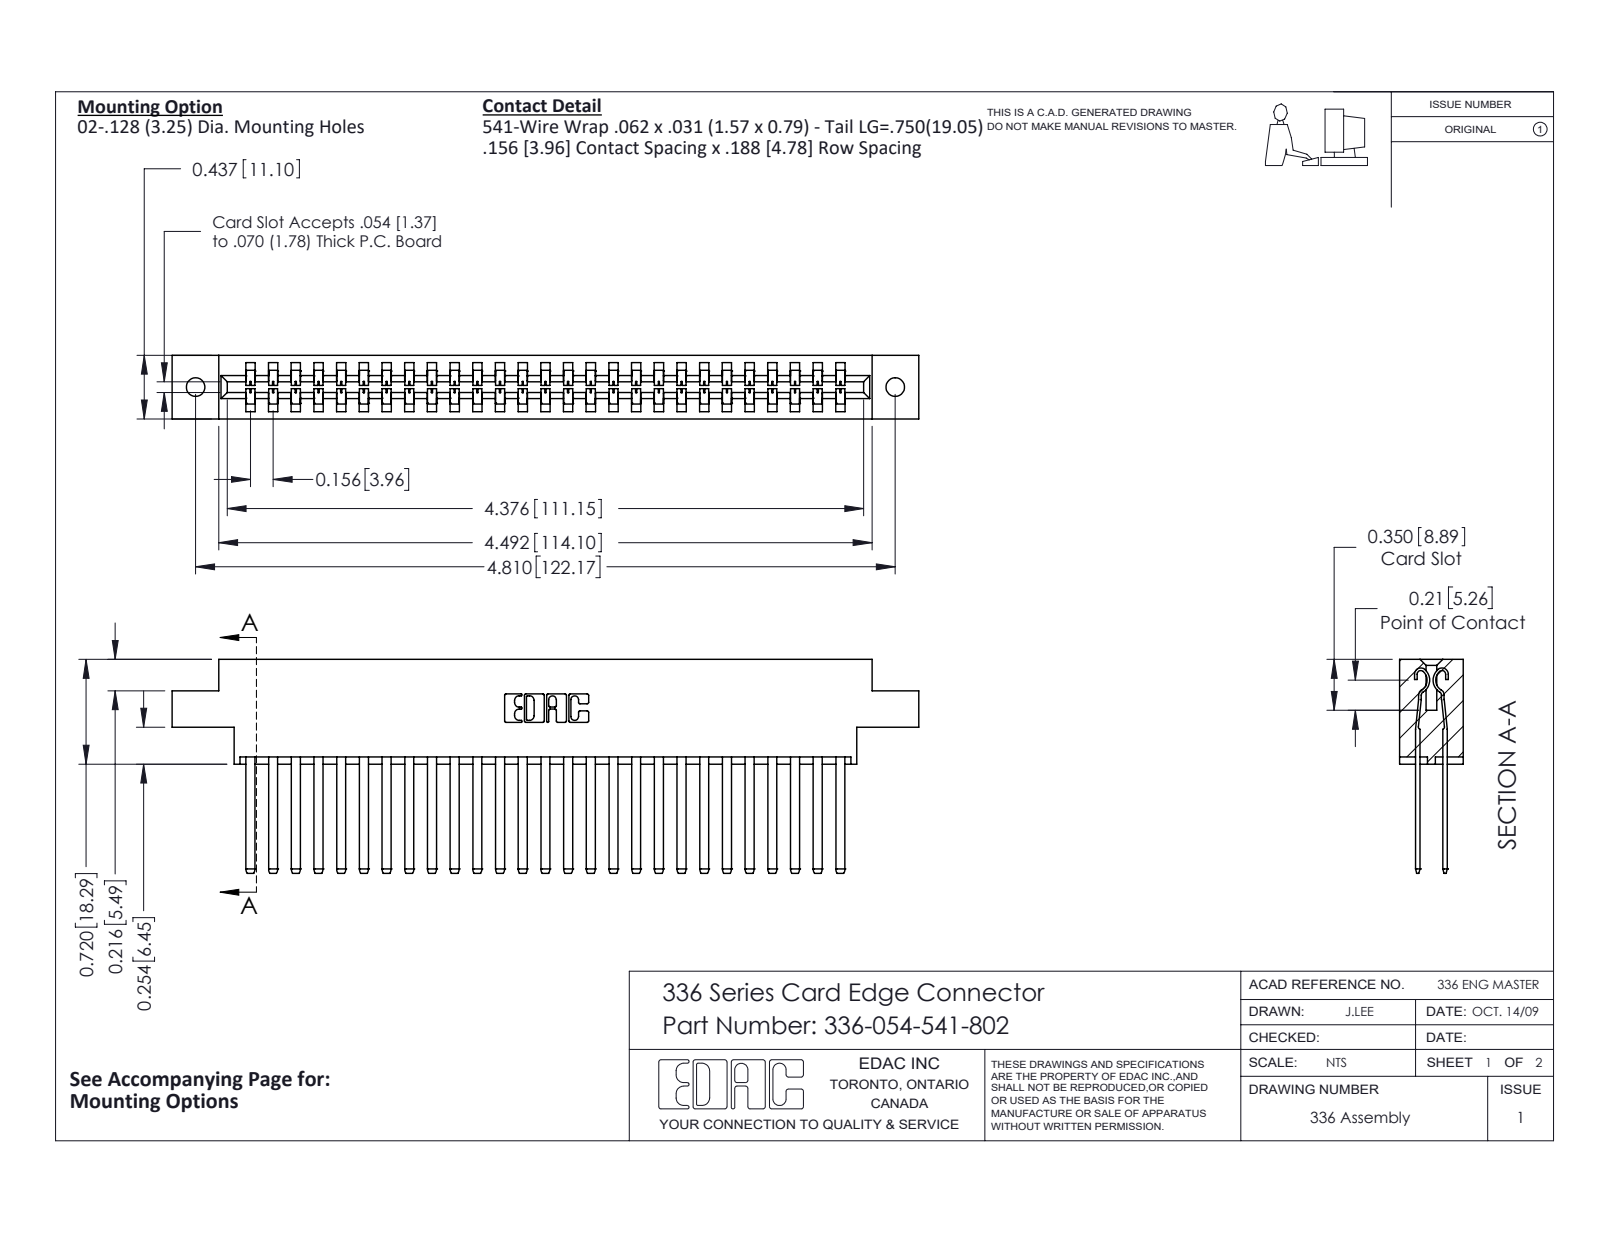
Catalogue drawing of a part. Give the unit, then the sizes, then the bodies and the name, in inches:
Units: inches
Overall size (bounding box): 5.133 × 1.47 × 0.437
Round holes (diameter × count): ⌀0.128 ×2
Partial cylindrical surfaces — rounded edges, fillets, slot ends (radius × count): R0.004 ×108, R0.056 ×54, R0.01 ×22, R0.007 ×6, R0.031 ×6, R0.022 ×4, R0.04 ×4, R0.026 ×3
Main face-to-face distances: 0.188, 0.328, 0.14, 0.297, 0.109, 0.031, 0.437, 0.033, 0.181, 0.256
Hole centre spacings: 4.81
Volume: 1.189 in³ · Surface area: 38.08 in²
Bodies: 55 solids, 2386 faces (1478 planar, 908 cylindrical, 0 other)
Part name (STEP PRODUCT): 336-054-541-802; 336 Part_Offset - .128 Dia; 336-290-001_336-290-541
STEP written by: SolidWorks 2020 (CONFIG_CONTROL_DESIGN)
